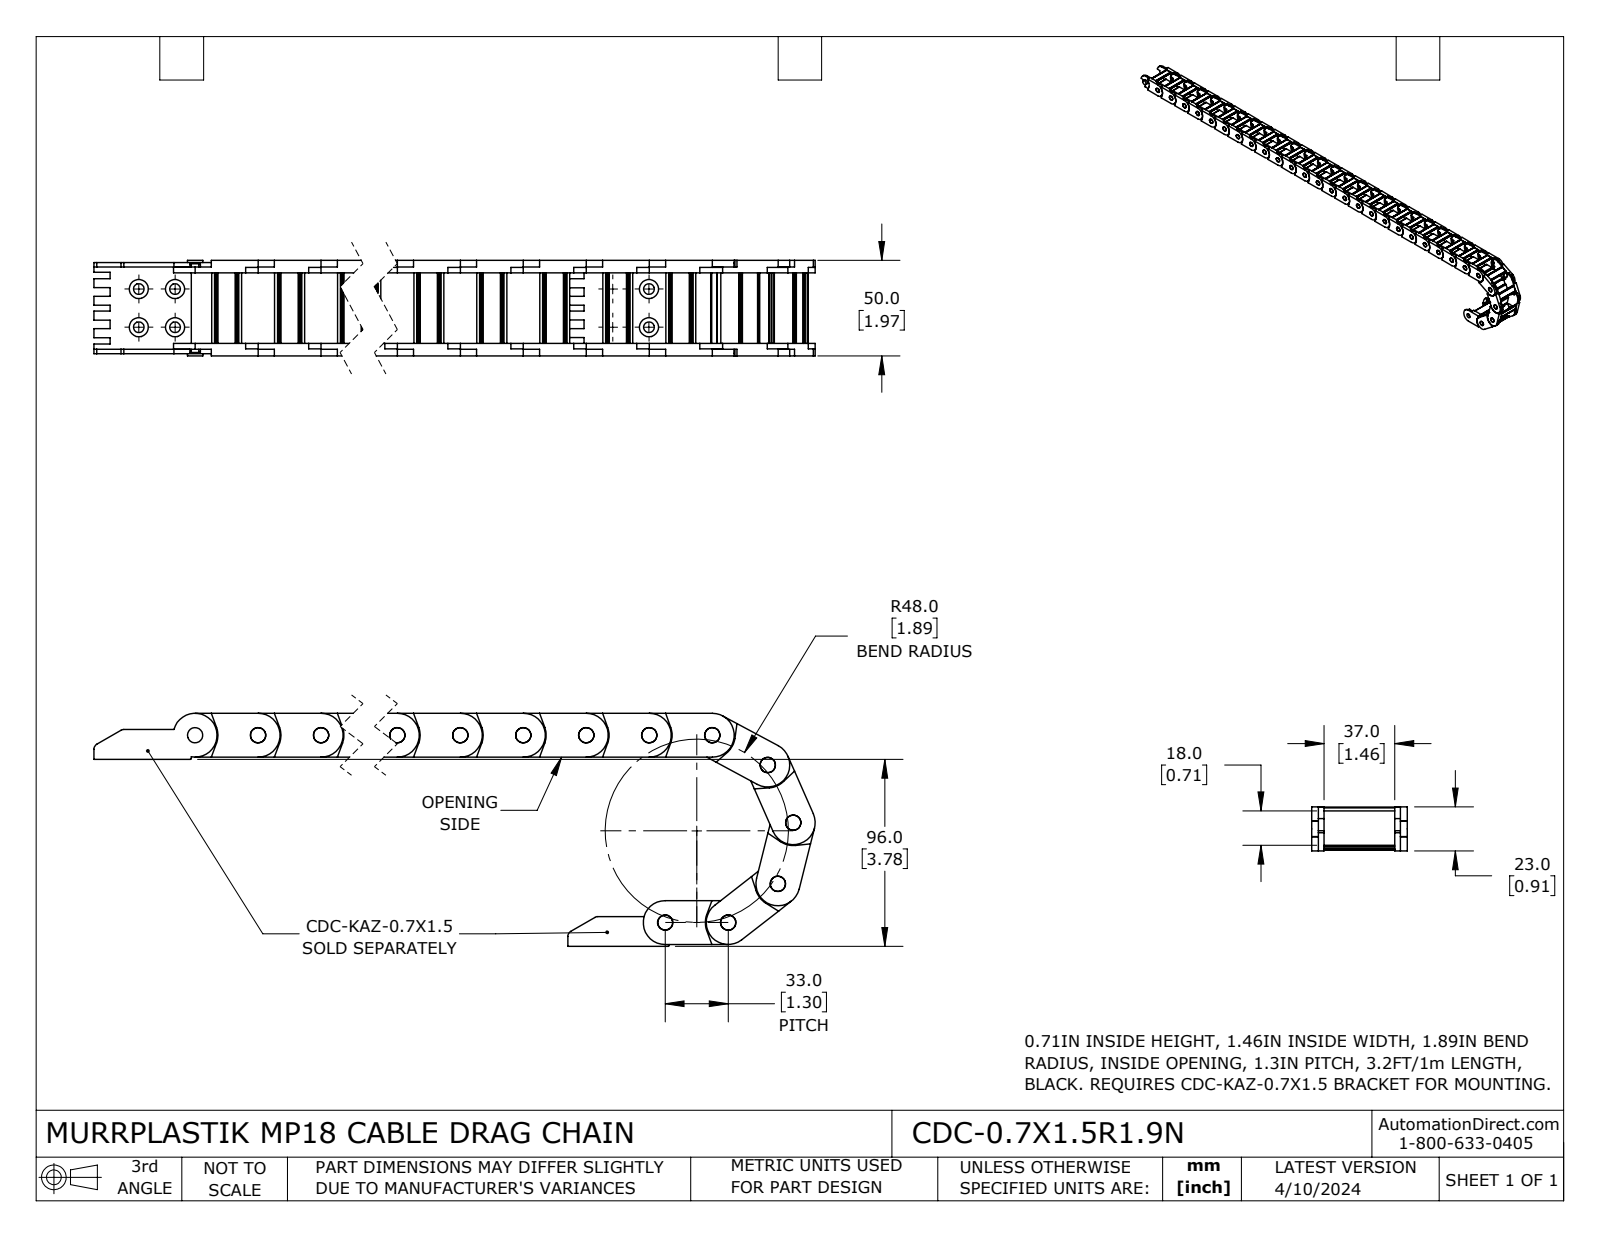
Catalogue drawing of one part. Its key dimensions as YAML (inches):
part_name: "CDC-0.7X1.5R1.9N"
step_written_by: "SolidWorks 2023 (CONFIG_CONTROL_DESIGN)"
units: inches
bodies: {solids: 30, faces: 2370, planar: 1110, cylindrical: 1260, other: 0}
overall_size: [35.048, 4.767, 1.969]
volume: 19.75
surface_area: 377.9
round_holes:
  - {diameter: 0.315, count: 30}
round_bosses_or_shafts:
  - {diameter: 0.315, count: 1}
partial_cylinders:
  - {radius: 0.02, count: 120}
  - {radius: 0.059, count: 120}
  - {radius: 0.008, count: 60}
  - {radius: 0.012, count: 60}
  - {radius: 0.453, count: 31}
  - {radius: 0.47, count: 31}
  - {radius: 0.197, count: 30}
  - {radius: 0.215, count: 30}
face_to_face_distances: [1.713, 0.256, 1.969, 0.138, 1.831, 0.118, 1.575, 0.146, 1.823, 1.685]
hole_center_spacings: [1.299, 2.598, 3.898, 5.197, 6.496, 7.795, 9.094, 10.394]
